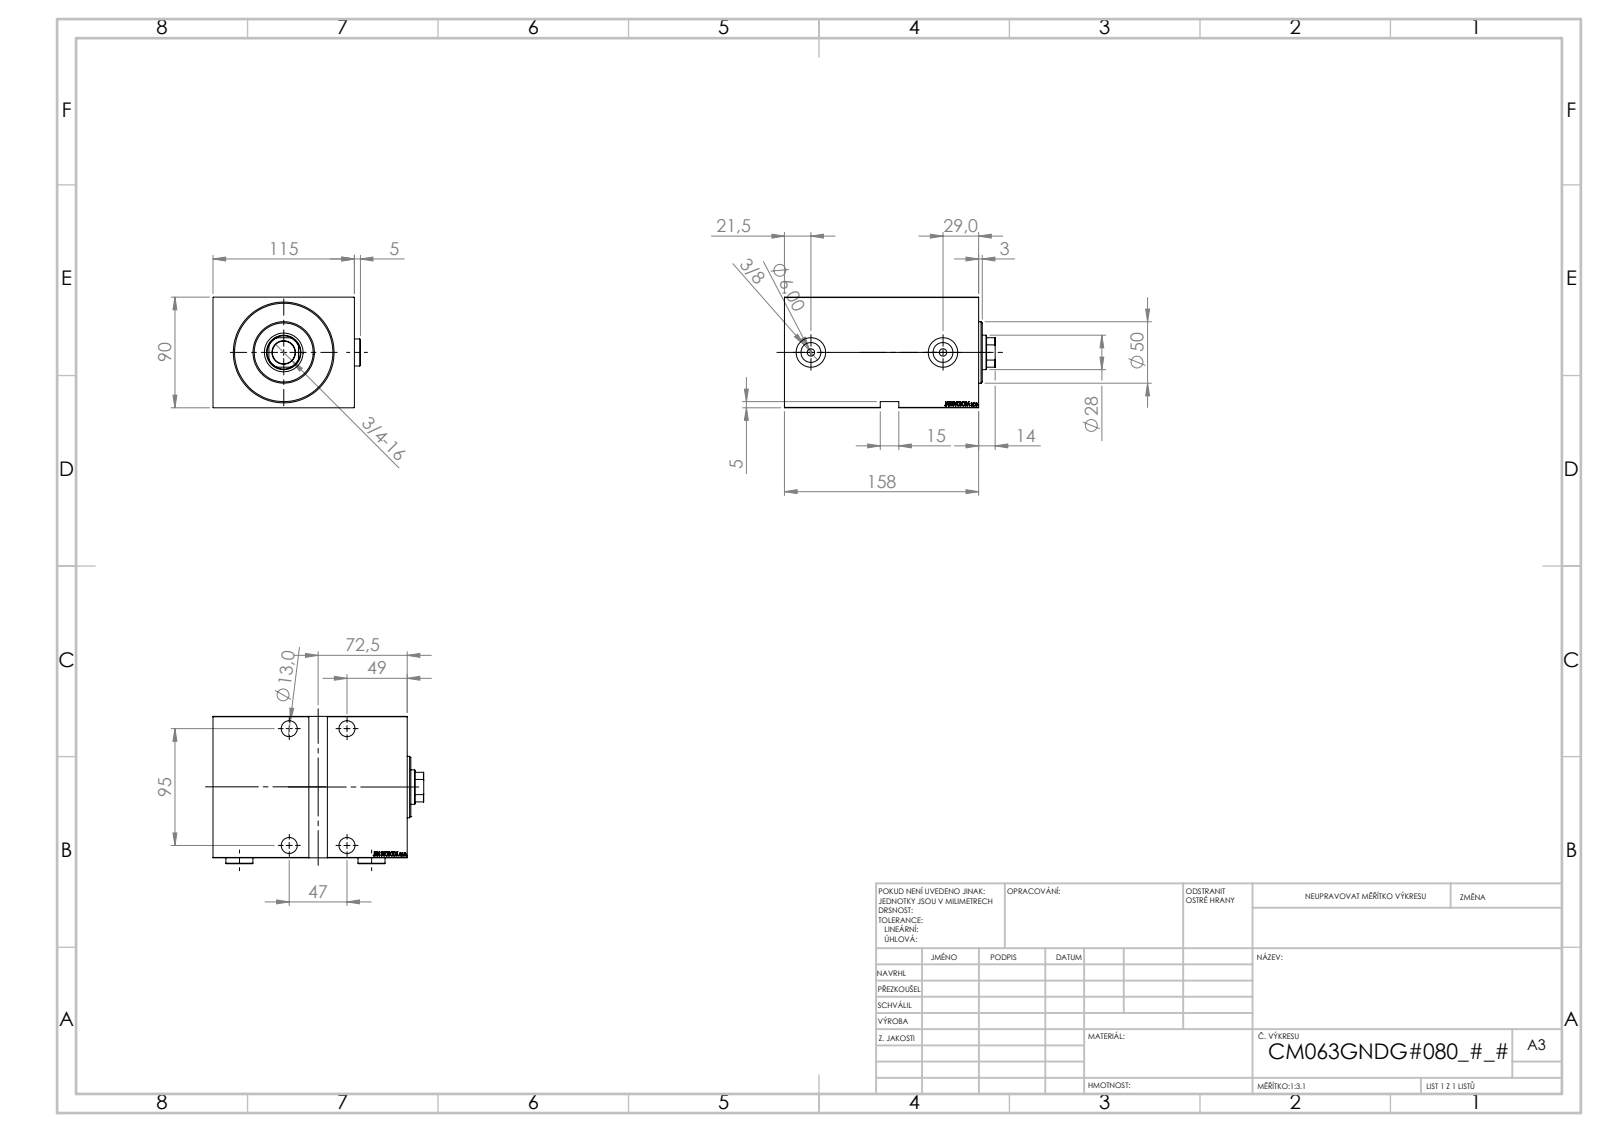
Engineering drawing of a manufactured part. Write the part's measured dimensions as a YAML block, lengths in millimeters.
part_name: "V450CM_VC_G; V450CM_G_Body; V450CM_G_VCP; Zatka_OIL_PORT"
step_written_by: "SolidWorks 2019 (CONFIG_CONTROL_DESIGN)"
units: millimeters
bodies: {solids: 5, faces: 912, planar: 446, cylindrical: 68, other: 398}
overall_size: [171.5, 119.9, 90]
volume: 1337000
surface_area: 173139
round_holes:
  - {diameter: 13, count: 4}
  - {diameter: 19, count: 4}
  - {diameter: 6, count: 2}
  - {diameter: 16.17, count: 2}
  - {diameter: 24, count: 2}
  - {diameter: 18.5, count: 1}
  - {diameter: 28, count: 1}
  - {diameter: 31.5, count: 1}
  - {diameter: 63, count: 1}
  - {diameter: 65, count: 1}
  - {diameter: 80, count: 1}
round_bosses_or_shafts:
  - {diameter: 22, count: 2}
  - {diameter: 50, count: 1}
partial_cylinders:
  - {radius: 13.5, count: 1}
face_to_face_distances: [90, 115, 5, 158, 17.5, 140.5, 153, 135.5, 93.5, 64.5]
hole_center_spacings: [47, 95, 105.99, 107.5]
